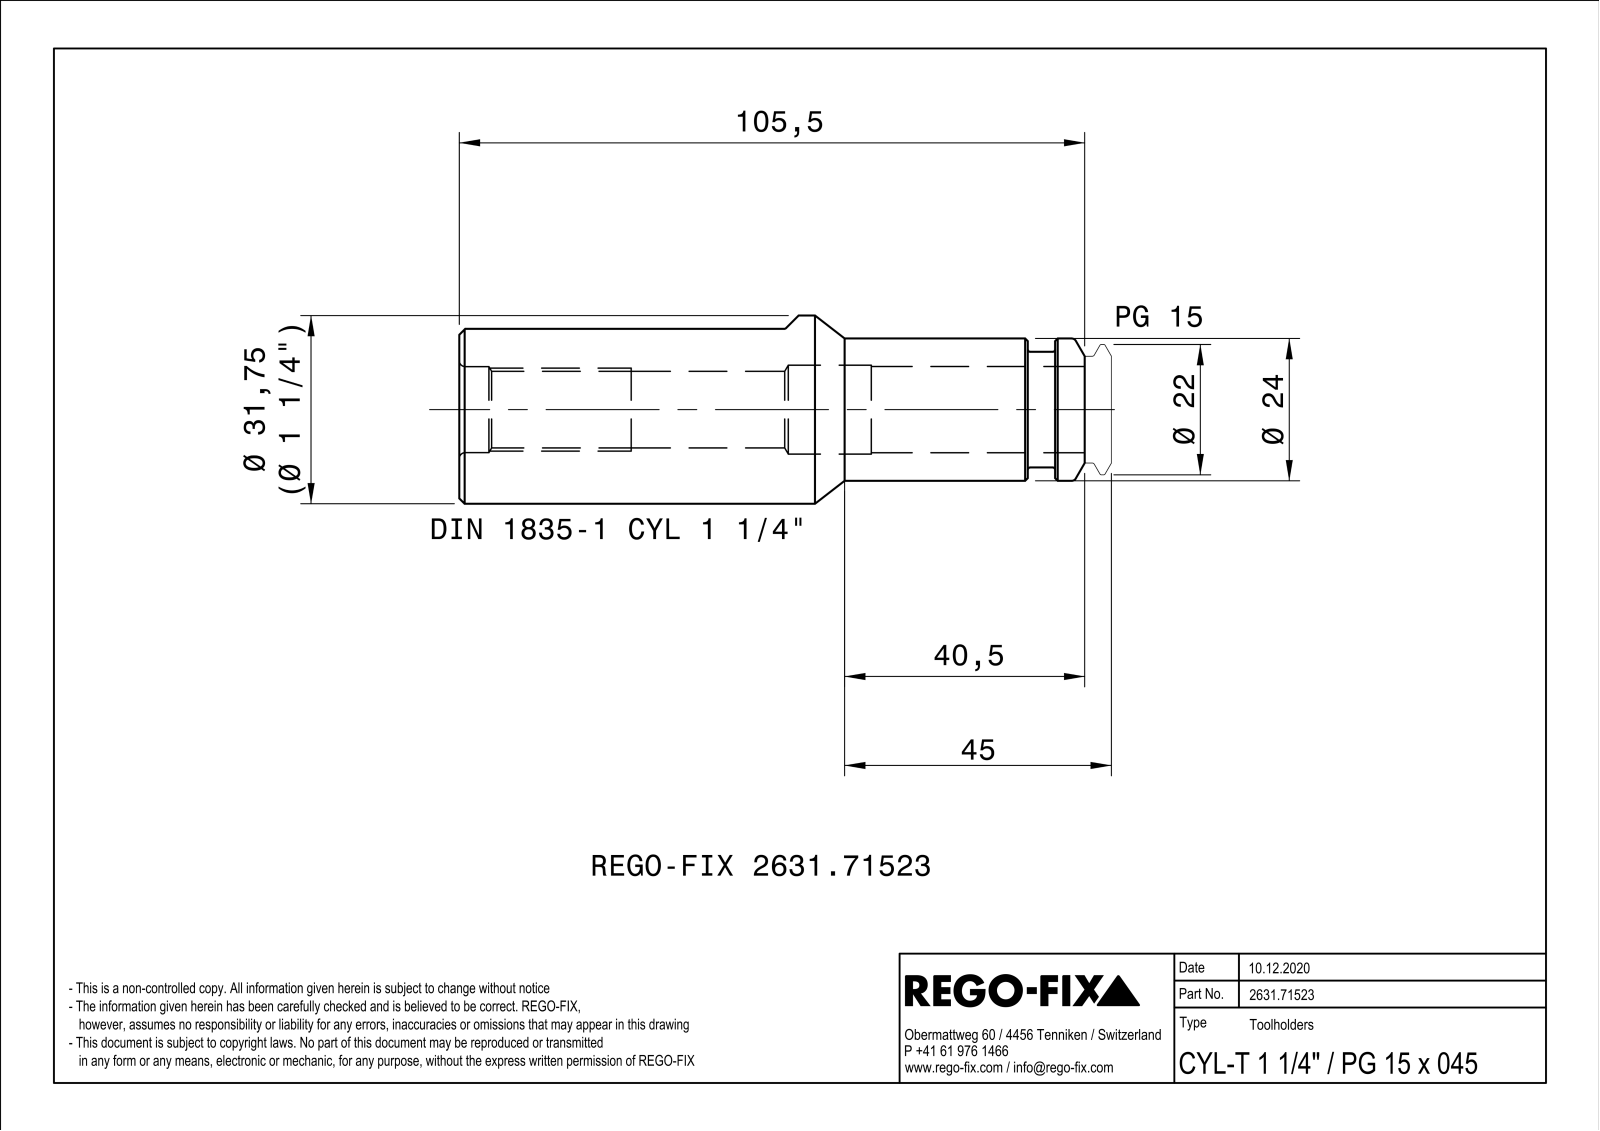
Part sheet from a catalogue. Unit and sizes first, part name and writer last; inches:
Units: inches
Overall size (bounding box): 4.154 × 1.25 × 1.25
Round holes (diameter × count): ⌀0.509 ×1, ⌀0.571 ×1, ⌀0.591 ×1
Round bosses / shafts (diameter × count): ⌀1.25 ×1, ⌀0.945 ×1, ⌀0.768 ×1
Partial cylindrical surfaces — rounded edges, fillets, slot ends (radius × count): R0.02 ×1
Main face-to-face distances: 3.776, 0.181, 3.957, 0.197, 0.378, 4.154, 1.503, 1.417, 1.22, 1.039
Volume: 3.077 in³ · Surface area: 23.38 in²
Bodies: 1 solid, 35 faces (8 planar, 10 cylindrical, 17 other)
Part name (STEP PRODUCT): NOCUT
STEP written by: SIEMENS PLM Software Solid Edge ST10 (AUTOMOTIVE_DESIGN)
